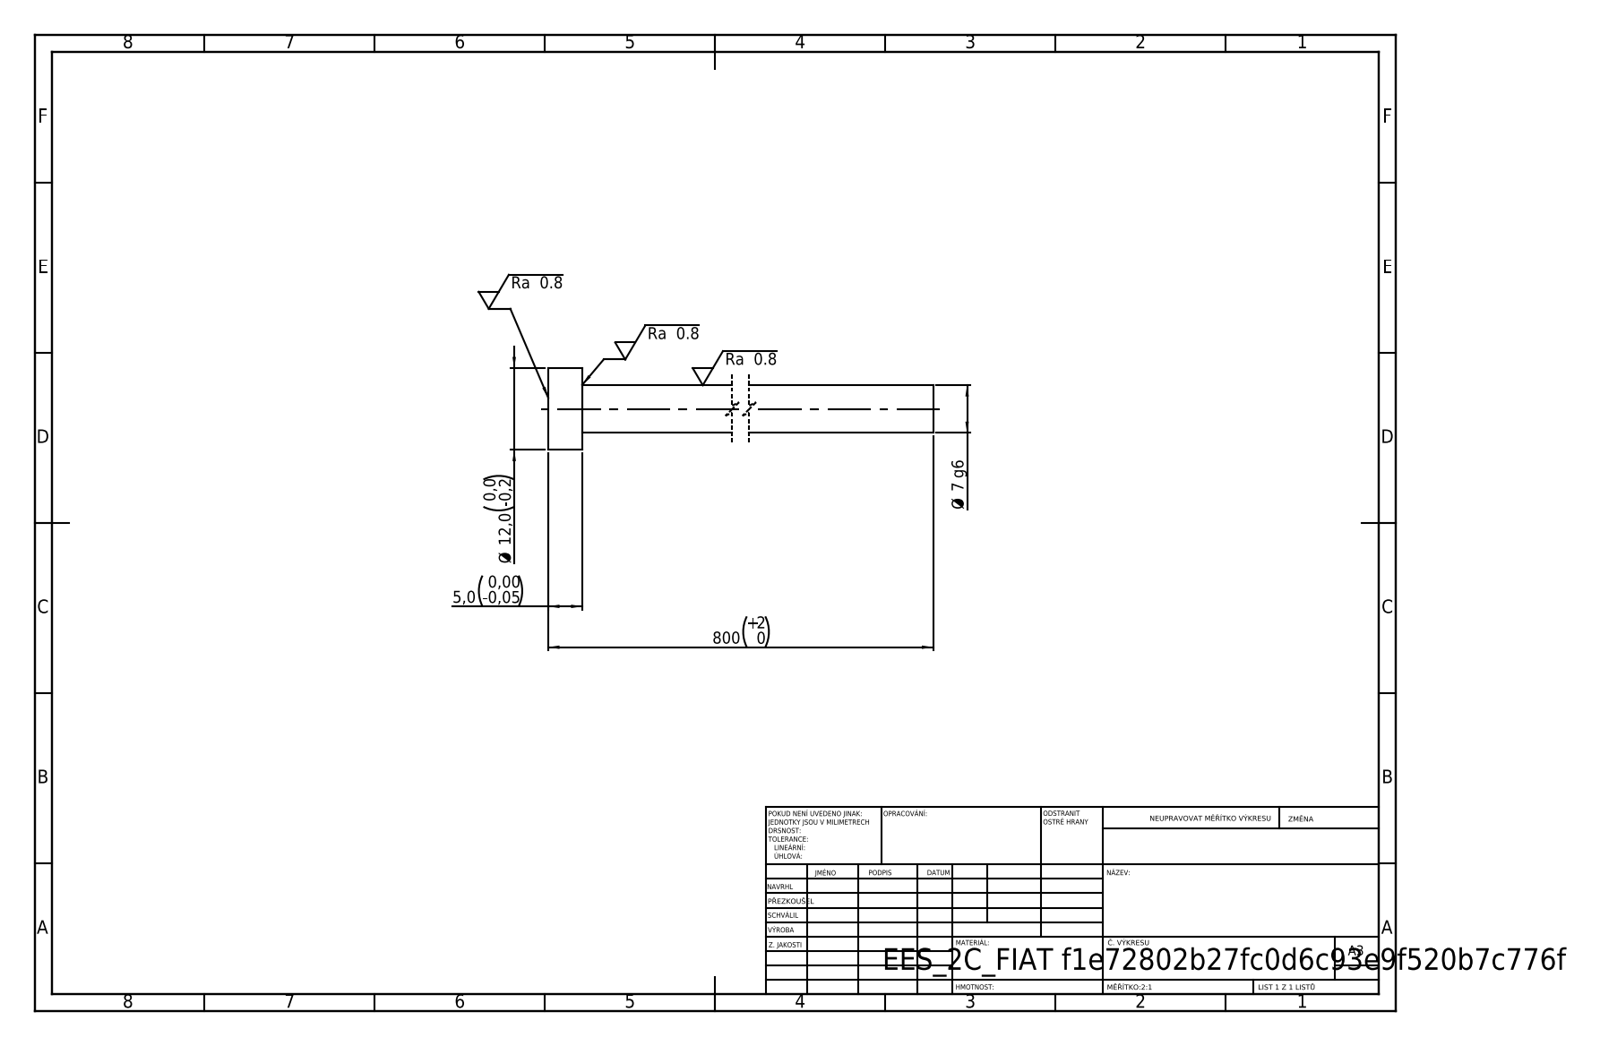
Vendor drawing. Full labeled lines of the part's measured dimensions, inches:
STEP written by: SolidWorks 2019 (CONFIG_CONTROL_DESIGN)
Units: inches
Bodies: 1 solid, 7 faces (3 planar, 4 cylindrical, 0 other)
Overall size (bounding box): 31.496 × 0.472 × 0.472
Volume: 1.902 in³ · Surface area: 27.74 in²
Round bosses / shafts (diameter × count): ⌀0.472 ×1, ⌀0.276 ×1
Main face-to-face distances: 0.197, 31.496, 31.299
